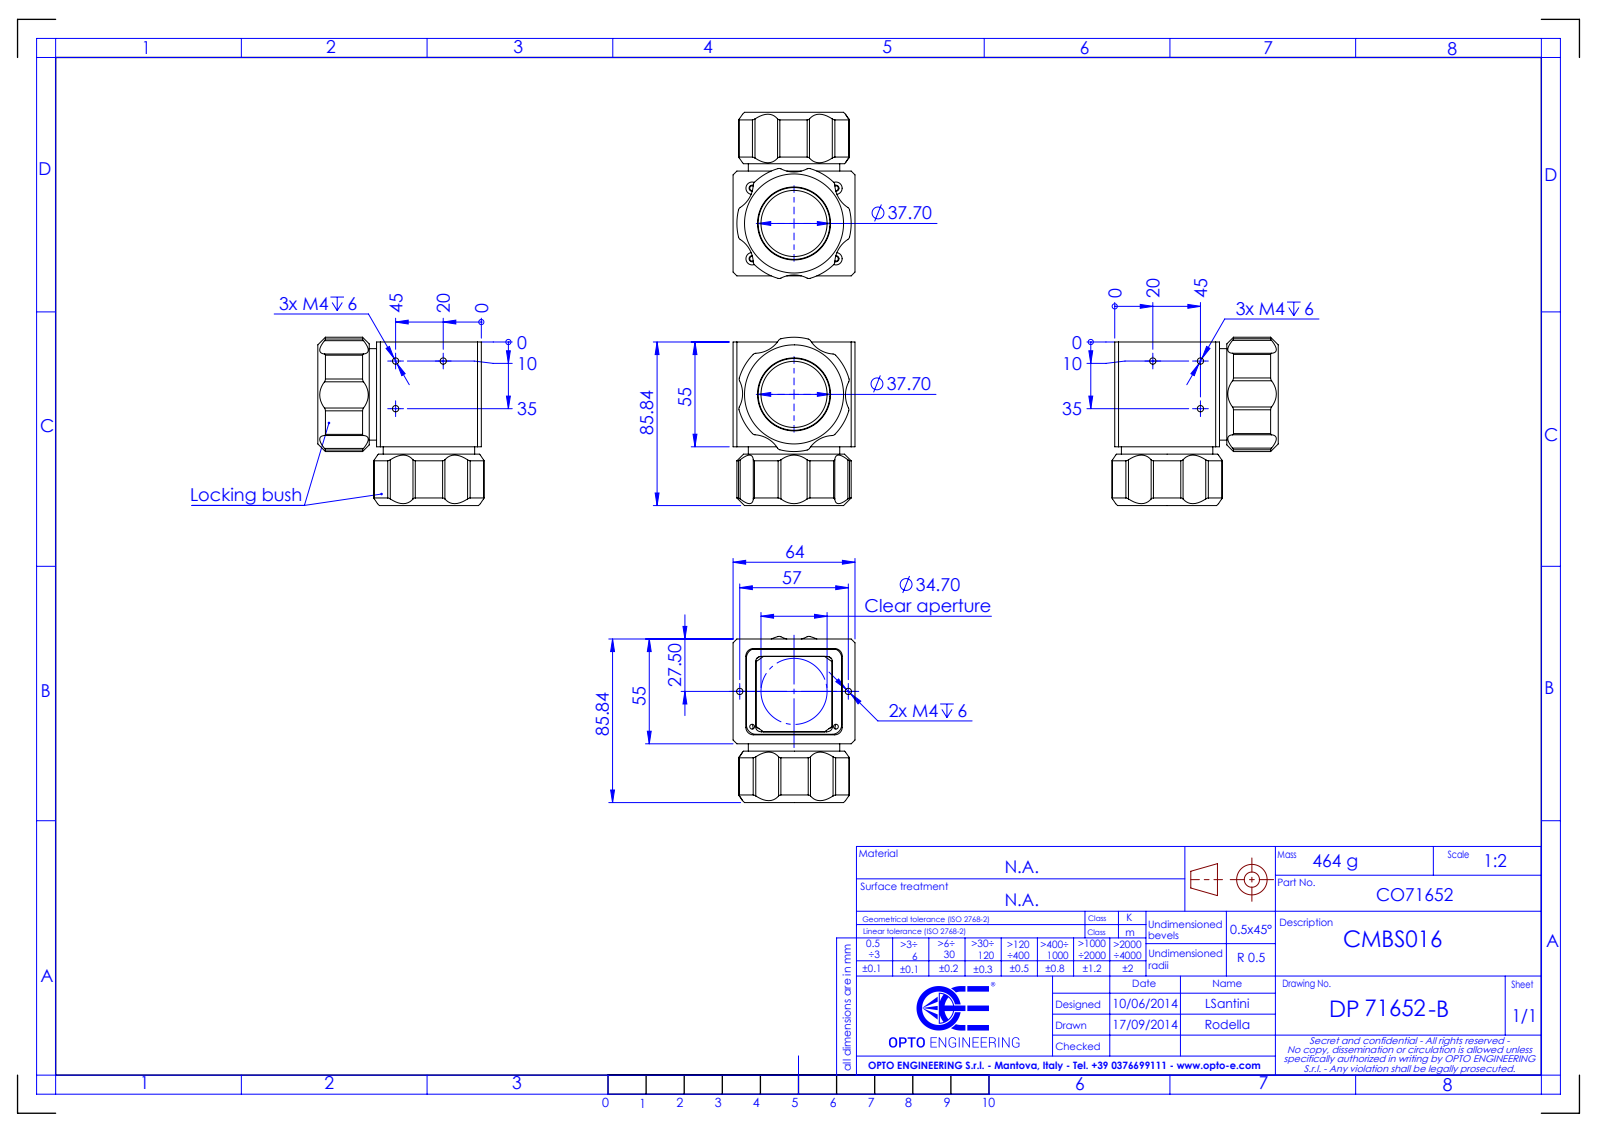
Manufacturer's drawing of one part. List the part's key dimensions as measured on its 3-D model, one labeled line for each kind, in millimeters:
Part name (STEP PRODUCT): DP71652-B_CMBS016
STEP written by: SolidWorks 2021 (CONFIG_CONTROL_DESIGN)
Units: millimetres
Bodies: 0 solids, 164 faces (39 planar, 104 cylindrical, 21 other)
Overall size (bounding box): 88.34 × 87.24 × 64
Round holes (diameter × count): ⌀3.3 ×5, ⌀3.2 ×4, ⌀6.5 ×4, ⌀37.7 ×2, ⌀38.3 ×2, ⌀34.7 ×1
Round bosses / shafts (diameter × count): ⌀48 ×2
Partial cylindrical surfaces — rounded edges, fillets, slot ends (radius × count): R2 ×24, R15 ×12, R4 ×4, R3 ×2, R30 ×2
Main face-to-face distances: 6.7, 57.3, 64, 55, 85.84, 30.84, 50.6, 45.3, 5, 50
Hole centre spacings: 19.61, 28.74, 53.78, 13, 25, 28.5, 37, 44
